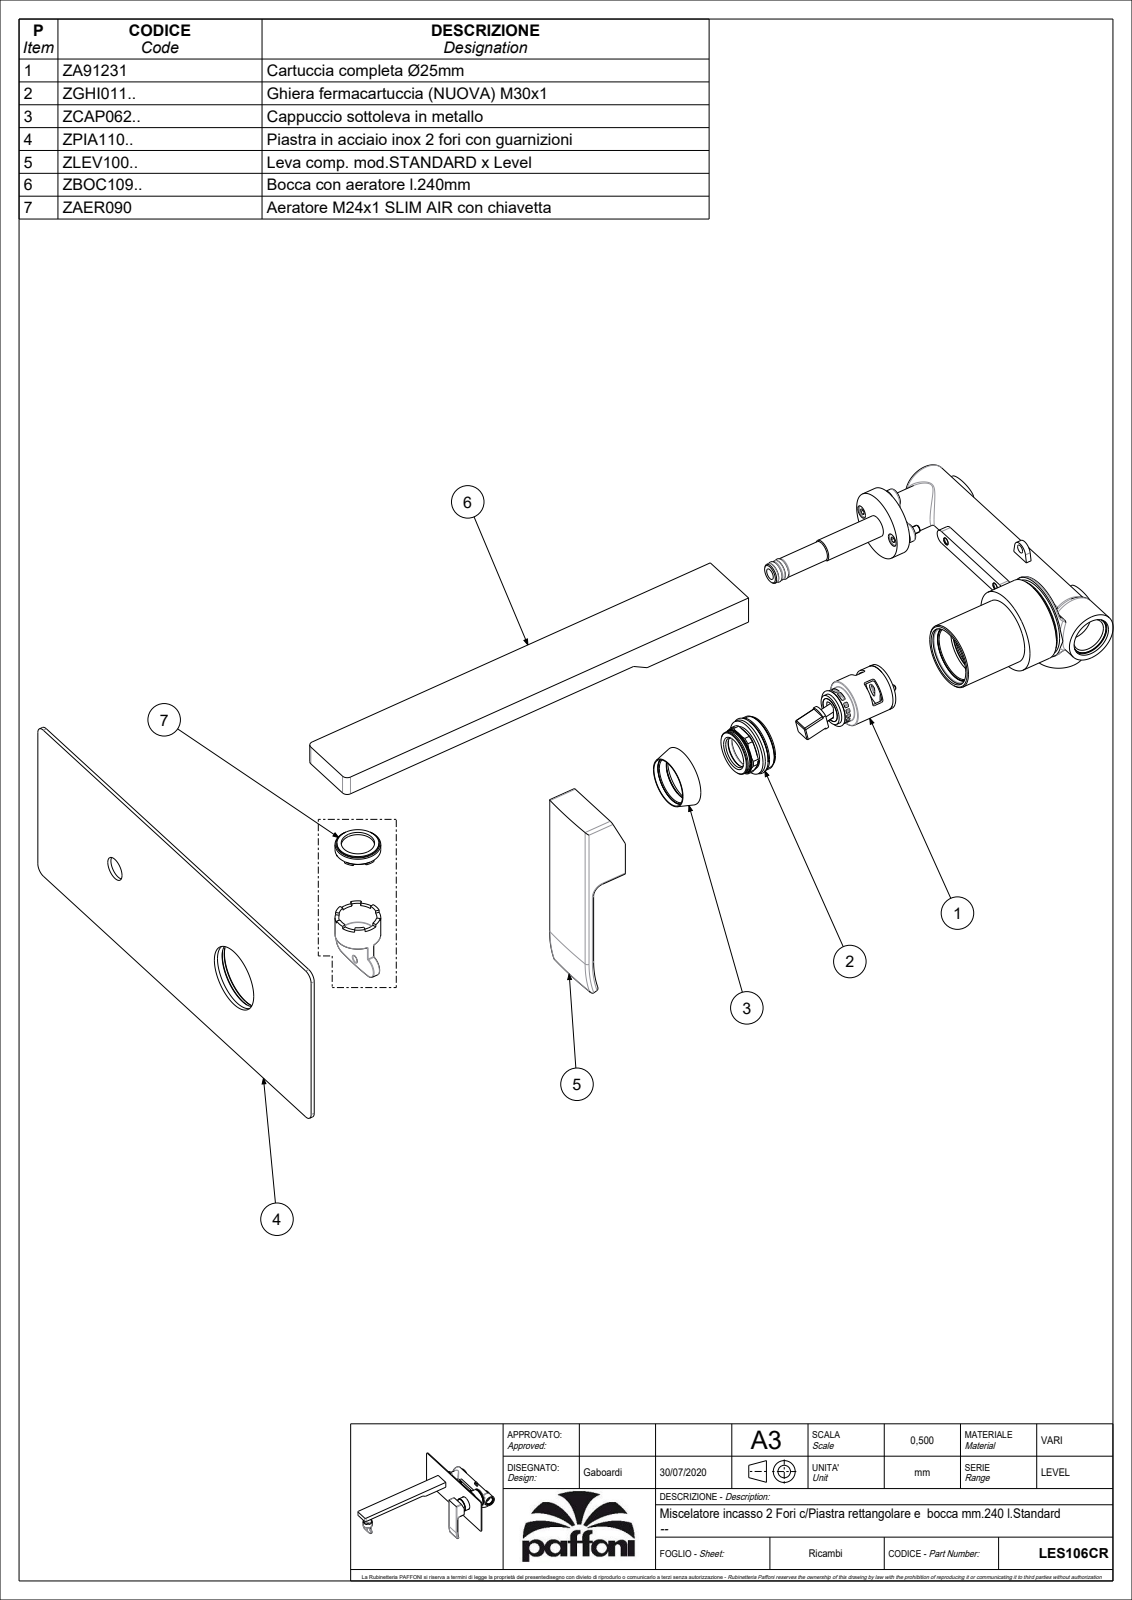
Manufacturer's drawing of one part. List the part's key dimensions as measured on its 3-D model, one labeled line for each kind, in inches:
Part name (STEP PRODUCT): LES106CR
STEP written by: CREO PARAMETRIC BY PTC INC, 2020044 (CONFIG_CONTROL_DESIGN)
Units: inches
Bodies: 2 solids, 740 faces (232 planar, 279 cylindrical, 229 other)
Overall size (bounding box): 10.236 × 9.843 × 5.565
Volume: 11.85 in³ · Surface area: 172.7 in²
Round holes (diameter × count): ⌀0.236 ×2, ⌀0.118 ×1, ⌀0.165 ×1, ⌀0.217 ×1, ⌀0.307 ×1, ⌀0.433 ×1, ⌀0.472 ×1, ⌀0.512 ×1, ⌀0.591 ×1, ⌀0.657 ×1, ⌀0.669 ×1, ⌀0.689 ×1
Round bosses / shafts (diameter × count): ⌀1.386 ×1, ⌀1.181 ×1, ⌀1.091 ×1, ⌀0.984 ×1, ⌀0.937 ×1, ⌀0.886 ×1, ⌀0.748 ×1, ⌀0.728 ×1
Partial cylindrical surfaces — rounded edges, fillets, slot ends (radius × count): R0.02 ×56, R0.079 ×16, R0.039 ×11, R0.059 ×8, R0.197 ×4, R0.083 ×2, R0.098 ×2, R0.118 ×2
Main face-to-face distances: 0.079, 0.453, 1.378, 0.197, 0.65, 4.291, 5.669, 2.913, 1.644, 2.293
Hole centre spacings: 4.291, 9.304
